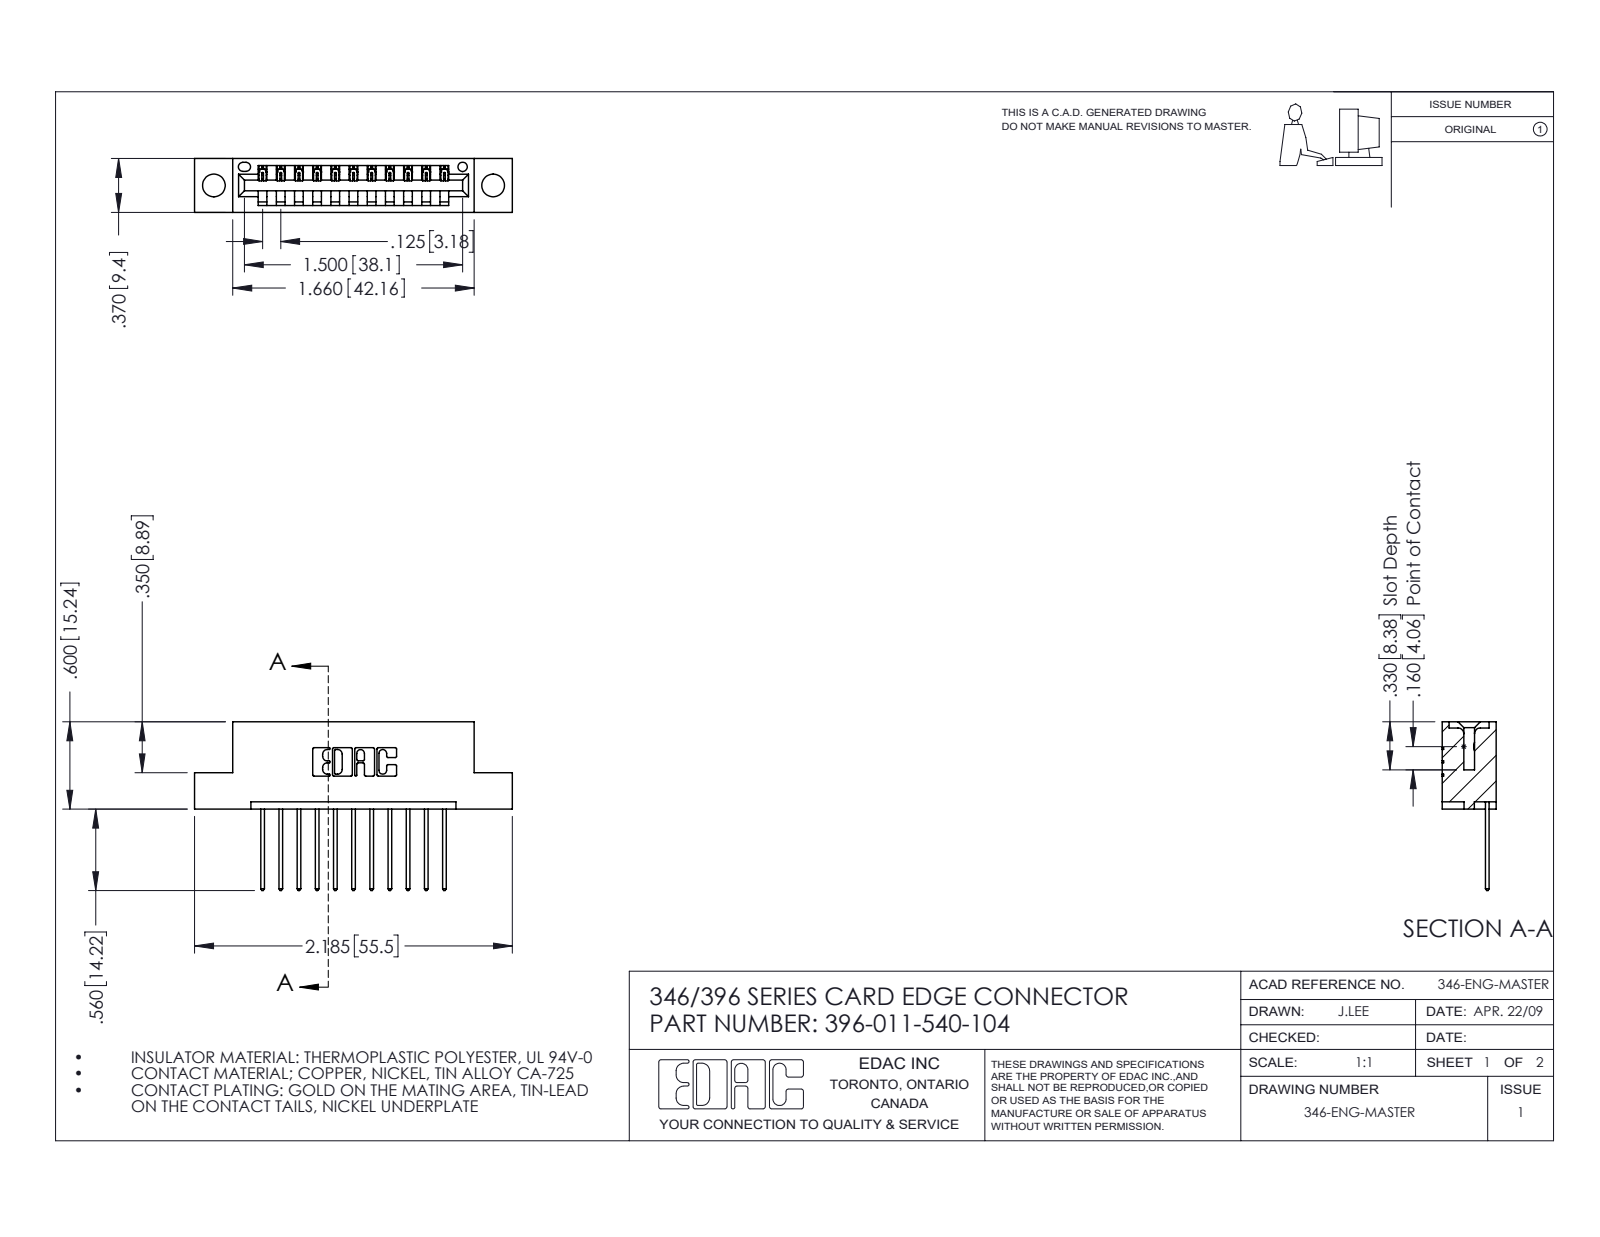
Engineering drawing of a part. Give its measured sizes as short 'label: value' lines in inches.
name: 345-292-001_345-293-140; 396-011-540-104; 346 Part_Flush Mounting Lugs - 0.156 Dia-TH
written by: SolidWorks 2016 (CONFIG_CONTROL_DESIGN)
unit: in
bodies: 12 solids, 760 faces (516 planar, 244 cylindrical, 0 other)
size: 2.185 × 1.16 × 0.37
volume: 0.307 in³; area: 9.085 in²
holes: 2× ⌀0.156, 1× ⌀0.064
rounds: 22× R0.006, 22× R0.01, 22× R0.01, 6× R0.007, 6× R0.031, 3× R0.026, 2× R0.031, 2× R0.04
face distances: 0.25, 0.048, 0.322, 0.37, 0.072, 0.298, 0.025, 0.148, 0.222, 0.1
hole spacings: 0.246, 1.715, 1.92
